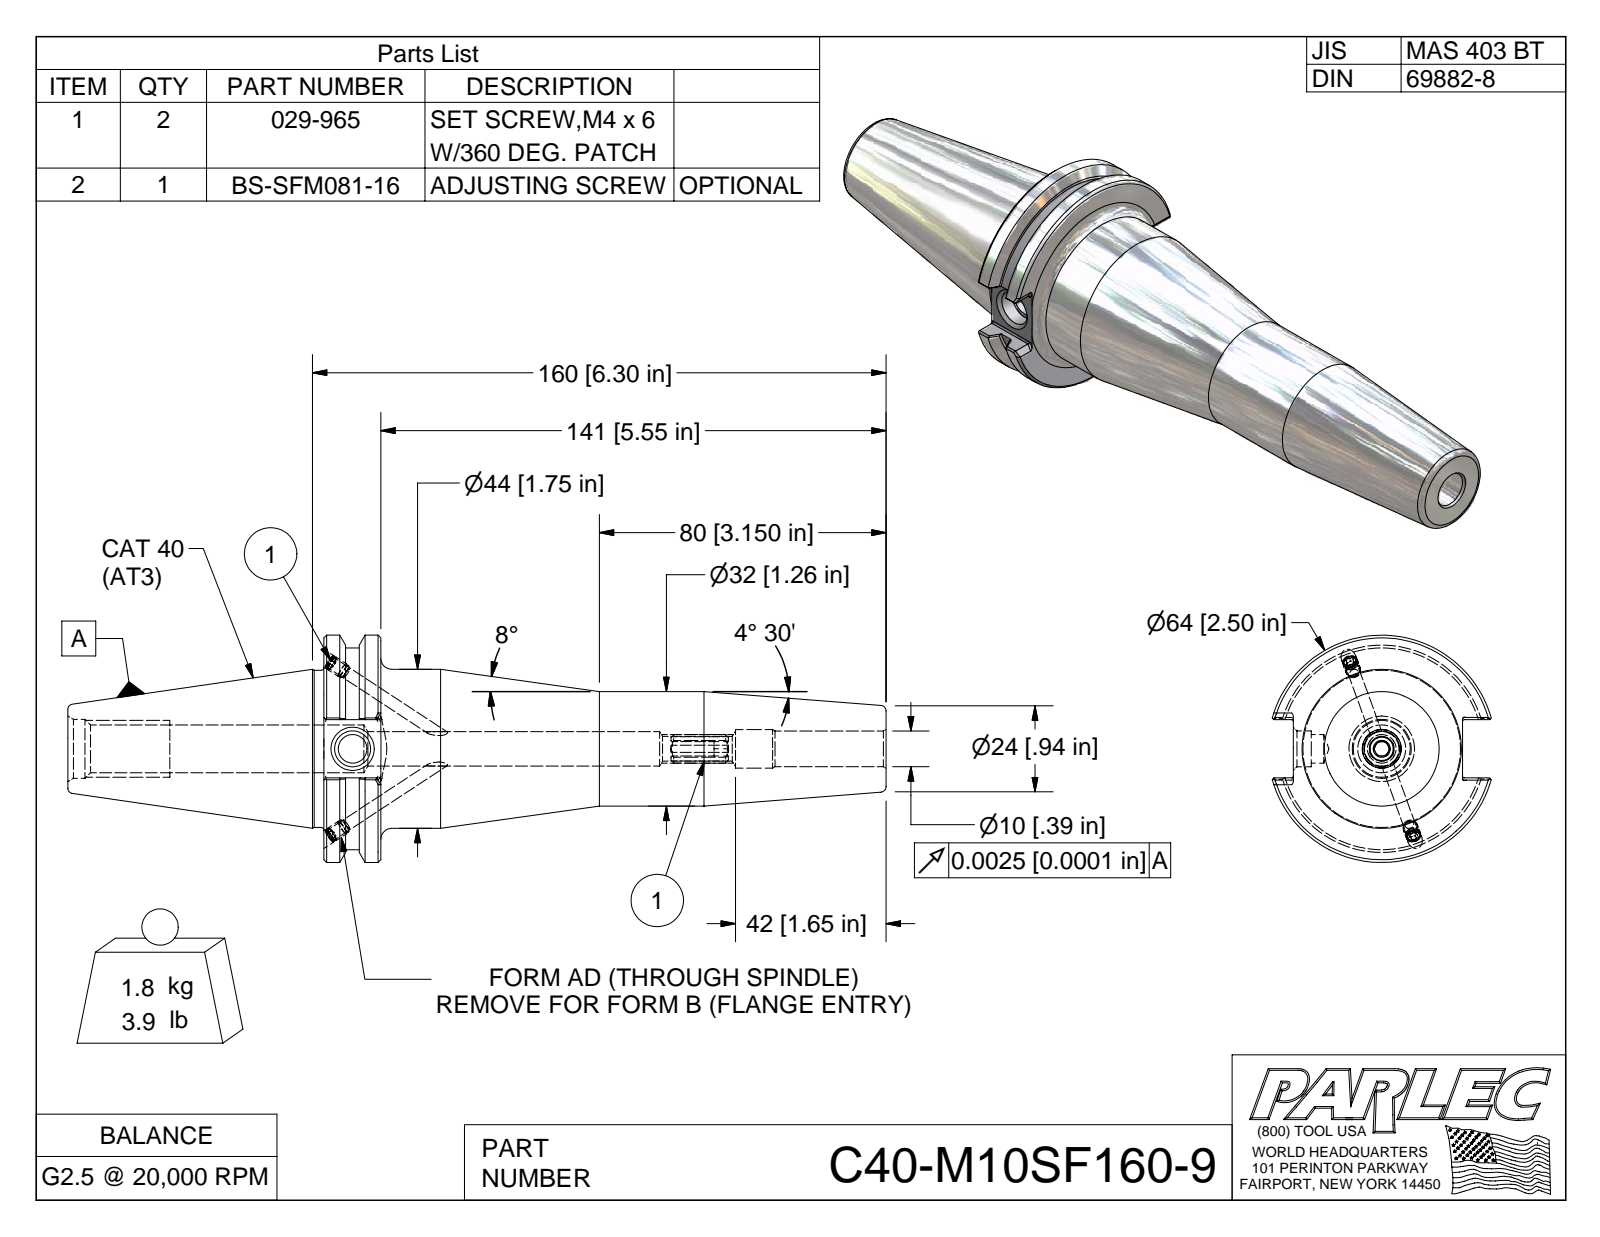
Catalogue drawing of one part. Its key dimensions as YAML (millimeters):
part_name: "C40-M10SF160-9; C40BC-M10SF160-9-1; 029-965; BS-SFM081-16"
step_written_by: "Autodesk Inventor 2009 (AUTOMOTIVE_DESIGN)"
units: millimeters
bodies: {solids: 4, faces: 155, planar: 66, cylindrical: 35, other: 54}
overall_size: [228.3, 63.5, 61.1]
volume: 223000
surface_area: 39880
round_holes:
  - {diameter: 3.3, count: 2}
  - {diameter: 4.1, count: 2}
  - {diameter: 10, count: 1}
  - {diameter: 10.7, count: 1}
round_bosses_or_shafts:
  - {diameter: 4.2, count: 2}
  - {diameter: 4, count: 2}
  - {diameter: 63.5, count: 1}
  - {diameter: 56.4, count: 1}
  - {diameter: 44.5, count: 1}
  - {diameter: 43.9, count: 1}
  - {diameter: 32, count: 1}
partial_cylinders:
  - {radius: 0.5, count: 12}
  - {radius: 4, count: 1}
face_to_face_distances: [15.9, 156.8, 141, 16.3, 47.2, 71.4, 87.3, 228.3, 6, 81.3]
